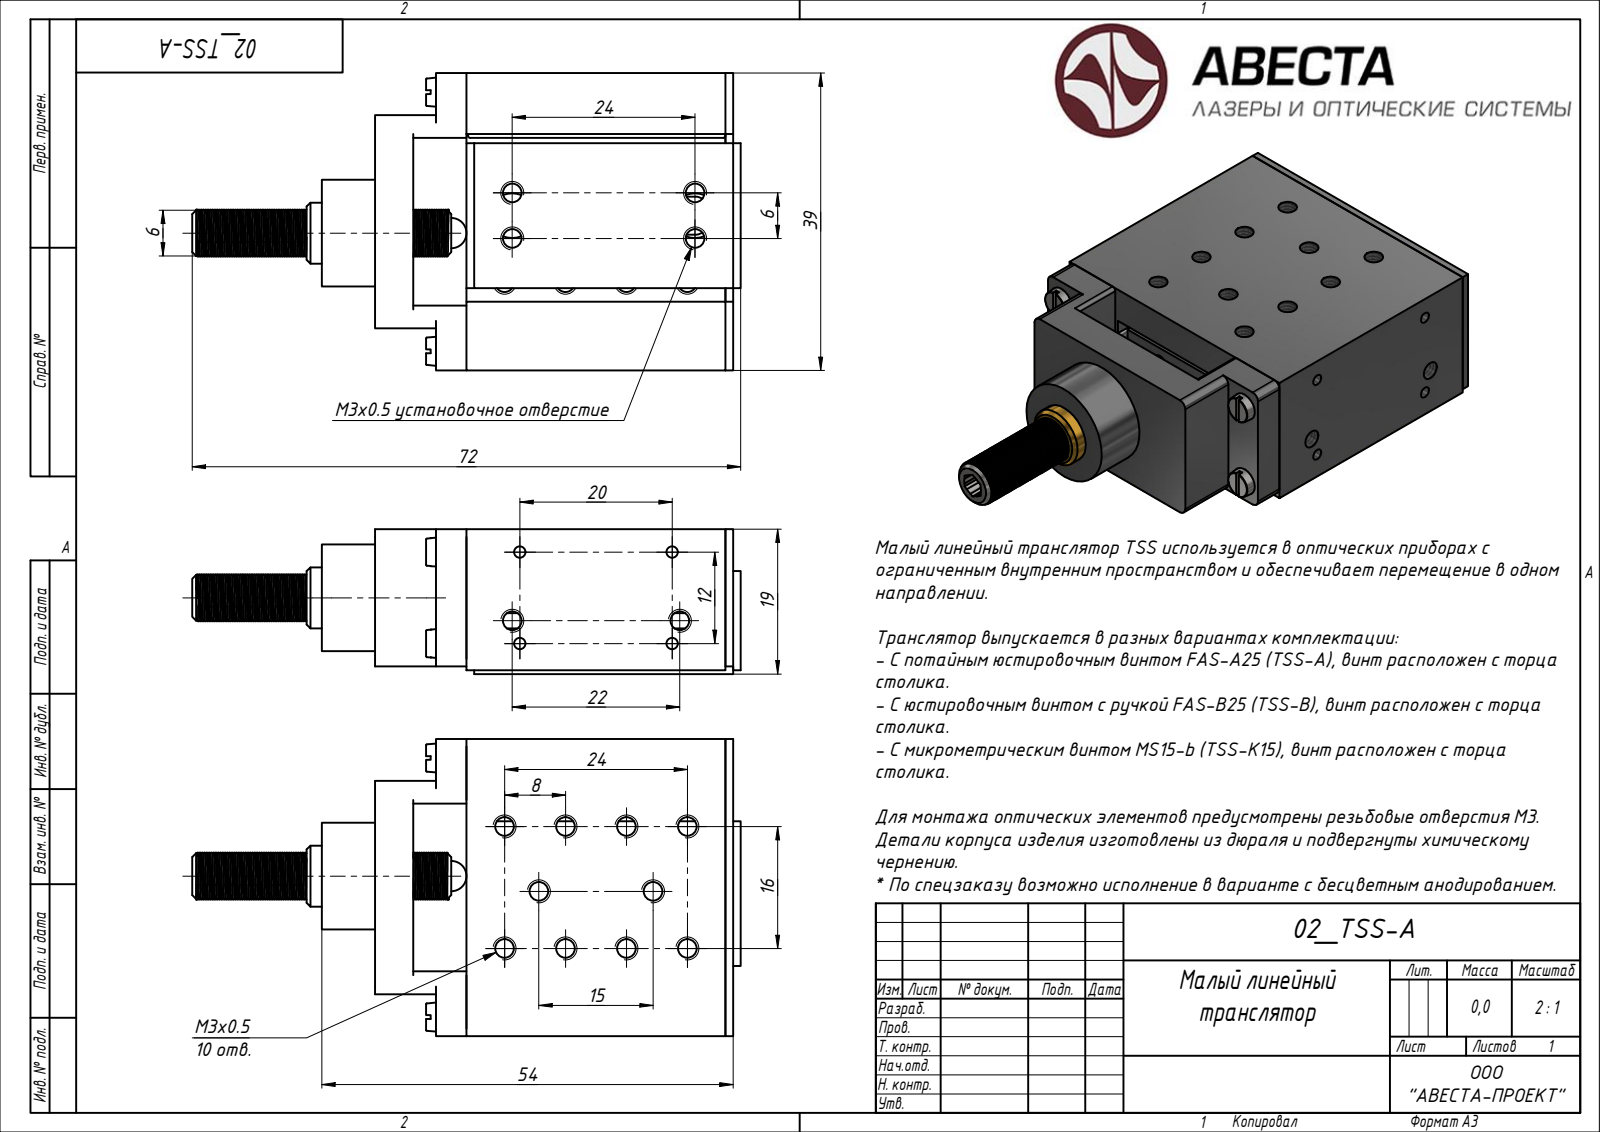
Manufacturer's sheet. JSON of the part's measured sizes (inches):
{"step_written_by": "Rhino 7.34 (AUTOMOTIVE_DESIGN)", "units": "inches", "bodies": {"solids": 2, "faces": 502, "planar": 135, "cylindrical": 263, "other": 104}, "overall_size": [2.835, 1.535, 0.748], "volume_in3": 1.582, "surface_area_in2": 29.33, "round_holes": [[0.097, 16], [0.098, 6], [0.062, 5], [0.059, 4], [0.062, 4], [0.097, 2], [0.122, 1], [0.236, 1], [0.374, 1]], "round_bosses_or_shafts": [[0.157, 8], [0.551, 1], [0.354, 1], [0.315, 1], [0.236, 1]], "partial_cylinders_radius": [[0.039, 8], [0.02, 4], [0.079, 4], [0.048, 2], [0.048, 2], [0.031, 1]], "face_to_face_distances": [0.02, 0.472, 0.197, 0.531, 0.079, 0.039, 0.059, 0.453, 0.276, 0.512], "hole_center_spacings": [0.63, 0.315, 0.704, 0.236, 0.276, 0.472, 0.124, 0.835]}
